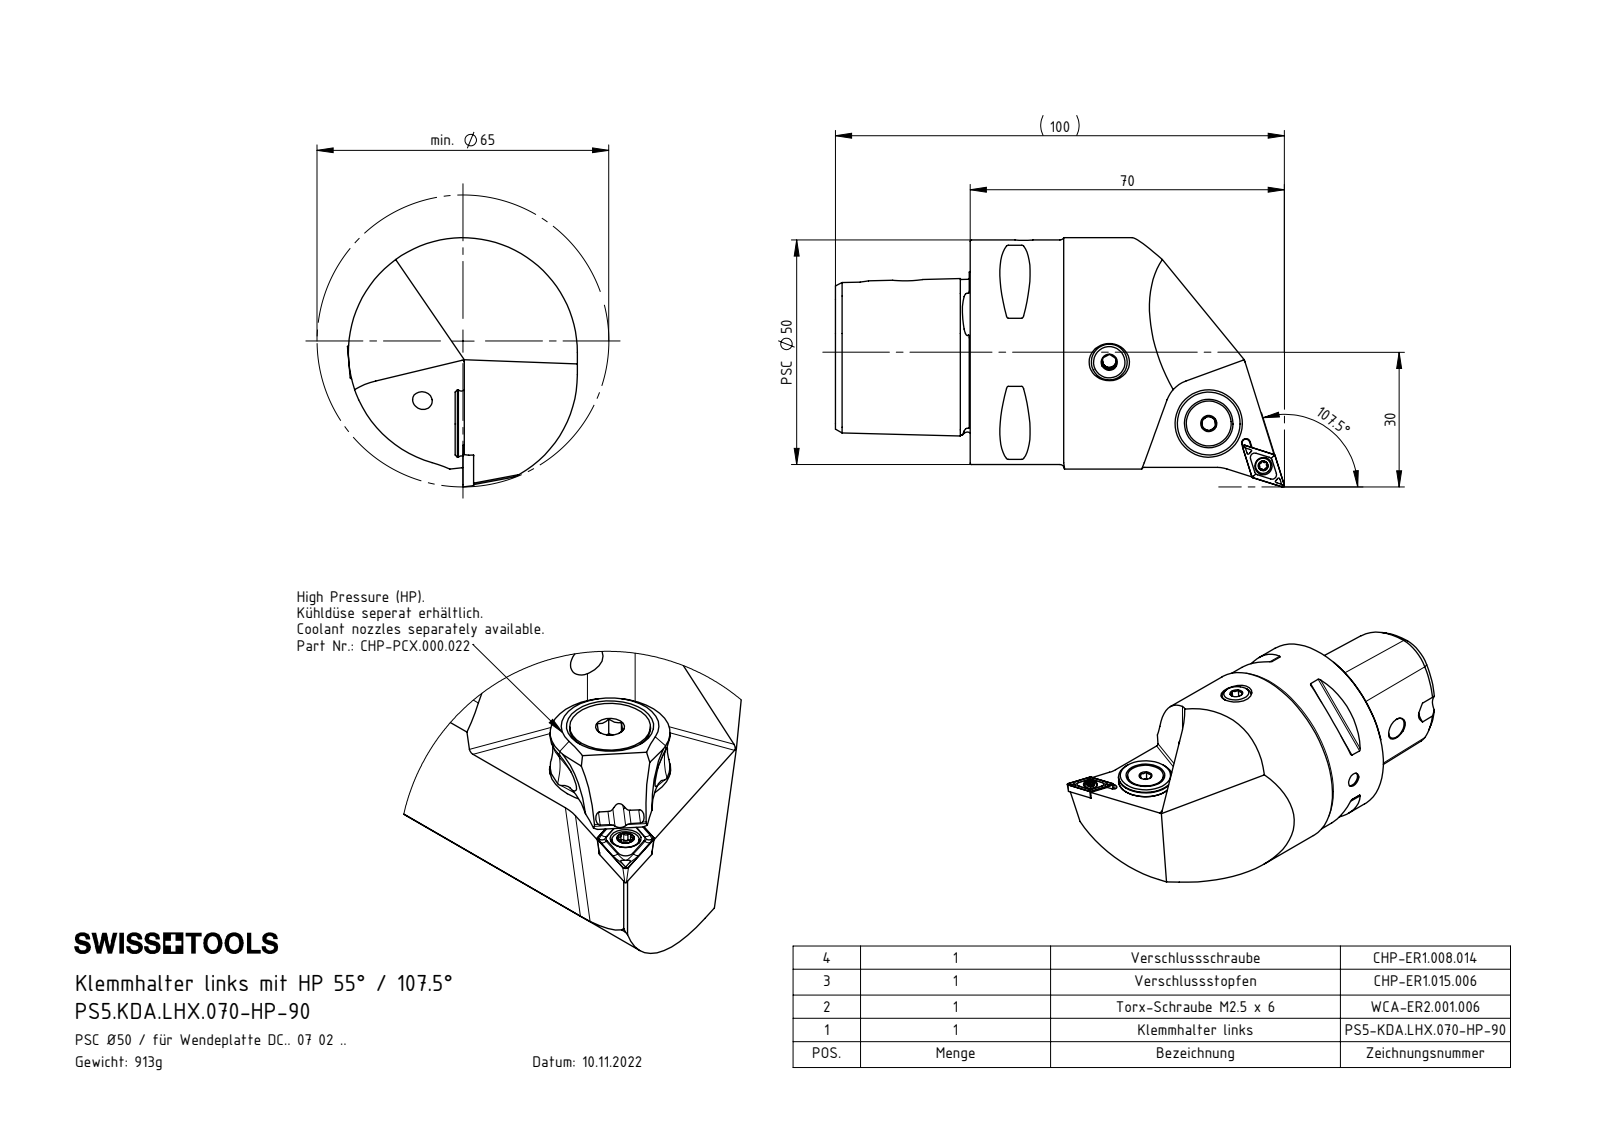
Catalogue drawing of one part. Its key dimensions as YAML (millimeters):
part_name: "DIN 7991 - M5x15; DCMT070204; WCA-ER2.001.006_B; DIN 3771 - 13x1 (+6 more)"
step_written_by: "SolidWorks 2017 (CONFIG_CONTROL_DESIGN)"
units: millimeters
bodies: {solids: 8, faces: 275, planar: 95, cylindrical: 66, other: 114}
overall_size: [99.99, 55.49, 51.21]
volume: 116219
surface_area: 23201
round_holes:
  - {diameter: 4.2, count: 3}
  - {diameter: 1.2, count: 1}
  - {diameter: 2, count: 1}
  - {diameter: 2.05, count: 1}
  - {diameter: 2.5, count: 1}
  - {diameter: 2.8, count: 1}
  - {diameter: 3, count: 1}
  - {diameter: 3.85, count: 1}
  - {diameter: 4, count: 1}
  - {diameter: 5, count: 1}
  - {diameter: 5.2, count: 1}
  - {diameter: 6.1, count: 1}
round_bosses_or_shafts:
  - {diameter: 50, count: 1}
  - {diameter: 15, count: 1}
  - {diameter: 13.4, count: 1}
  - {diameter: 10, count: 1}
  - {diameter: 8, count: 1}
  - {diameter: 5.5, count: 1}
  - {diameter: 5, count: 1}
  - {diameter: 3.4, count: 1}
partial_cylinders:
  - {radius: 0.5, count: 10}
  - {radius: 0.21, count: 6}
  - {radius: 0.36, count: 5}
  - {radius: 7, count: 2}
  - {radius: 25.5, count: 2}
  - {radius: 0.36, count: 1}
  - {radius: 0.85, count: 1}
  - {radius: 4, count: 1}
face_to_face_distances: [30, 4.5, 20.7, 25.2, 19.18, 44.4, 10, 20, 2.42, 23.12]
hole_center_spacings: [4.5, 6.36, 12.05, 12.14, 15.34, 15.44, 18.4, 18.5]
